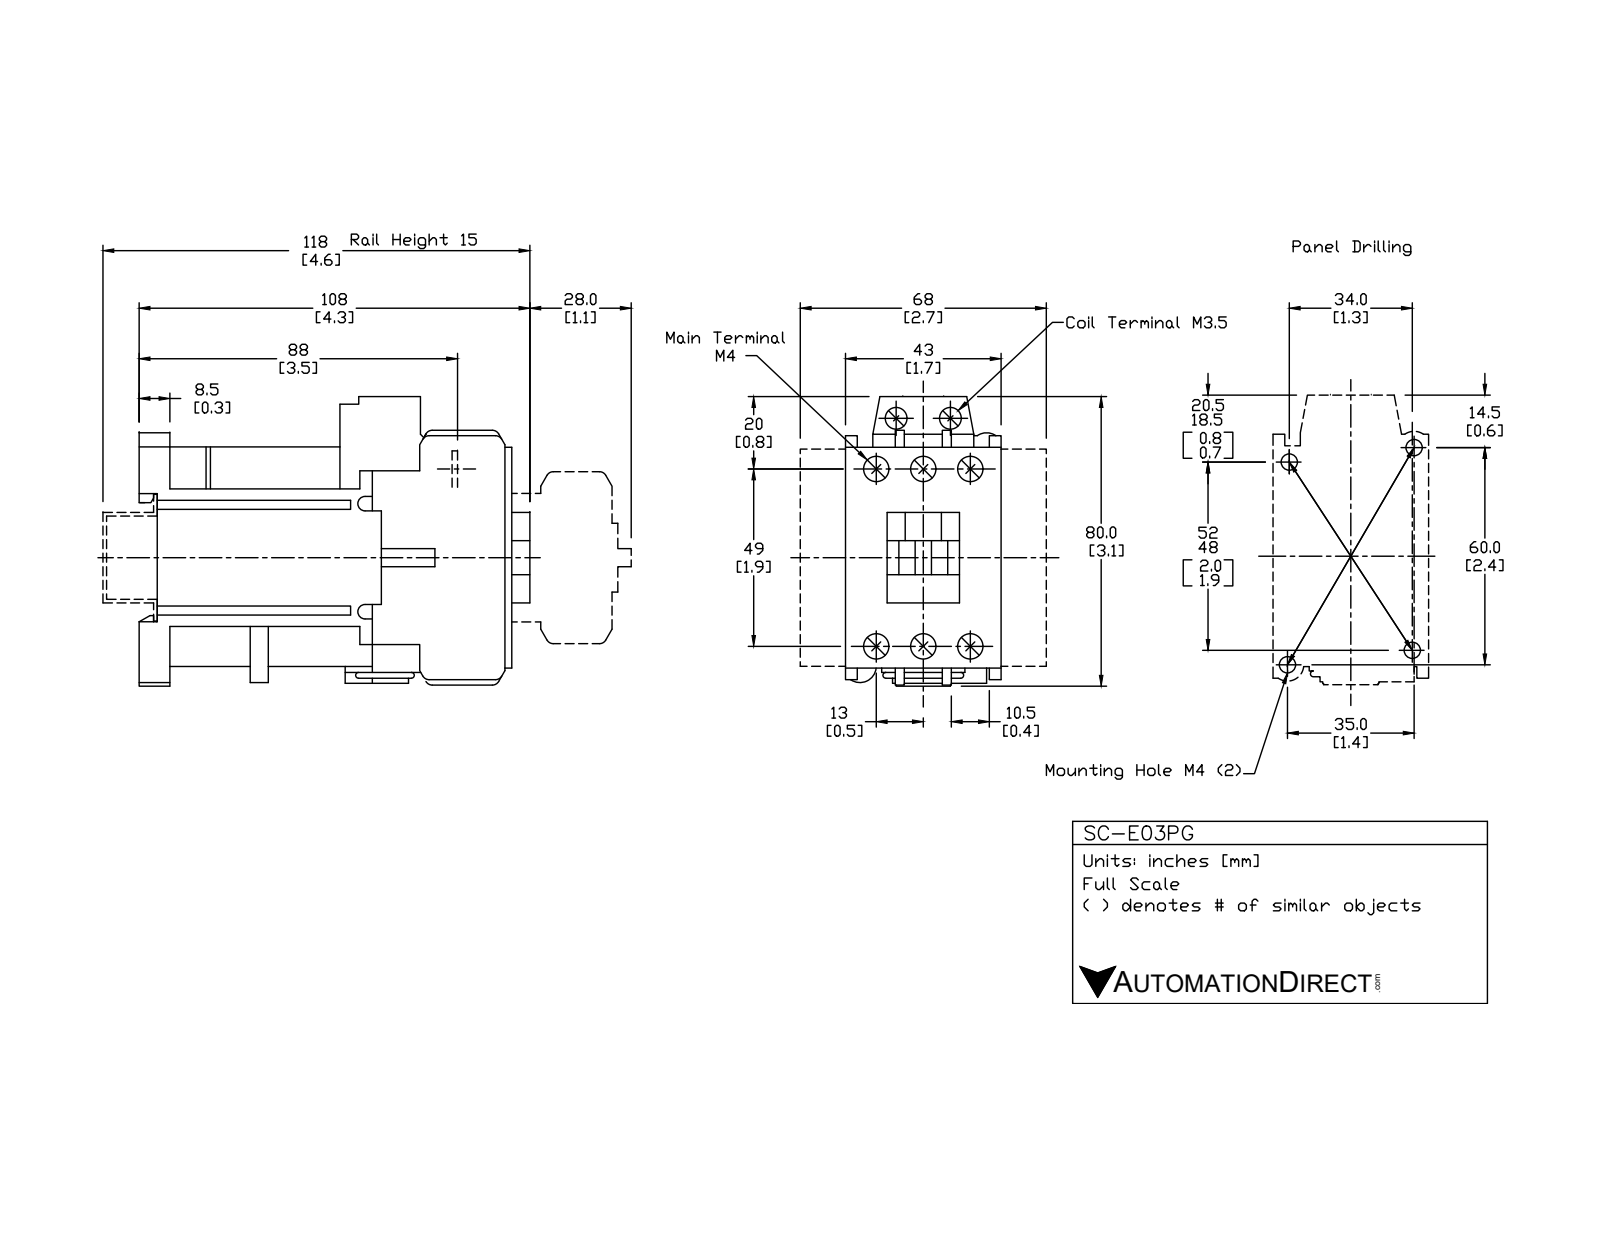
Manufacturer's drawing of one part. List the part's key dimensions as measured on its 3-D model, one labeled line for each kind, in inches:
Part name (STEP PRODUCT): SC-E03G-24VDC
STEP written by: SolidWorks 2015 (AUTOMOTIVE_DESIGN)
Units: inches
Bodies: 32 solids, 1701 faces (1440 planar, 213 cylindrical, 48 other)
Overall size (bounding box): 4.252 × 3.22 × 1.693
Volume: 13.95 in³ · Surface area: 94.1 in²
Round holes (diameter × count): ⌀0.157 ×6, ⌀0.161 ×6, ⌀0.276 ×6, ⌀0.138 ×2, ⌀0.142 ×2, ⌀0.189 ×2, ⌀0.264 ×2, ⌀0.063 ×1
Round bosses / shafts (diameter × count): ⌀0.299 ×6, ⌀0.26 ×2
Partial cylindrical surfaces — rounded edges, fillets, slot ends (radius × count): R0.059 ×32, R0.02 ×12, R0.079 ×11, R0.039 ×8, R0.024 ×4, R0.118 ×4, R0.177 ×4, R0.134 ×3
Main face-to-face distances: 1.693, 0.394, 0.65, 1.299, 0.138, 0.075, 0.256, 0.039, 0.02, 0.906
Hole centre spacings: 0.512, 1.996, 1.929, 0.268, 0.298, 0.592, 0.625, 0.704
